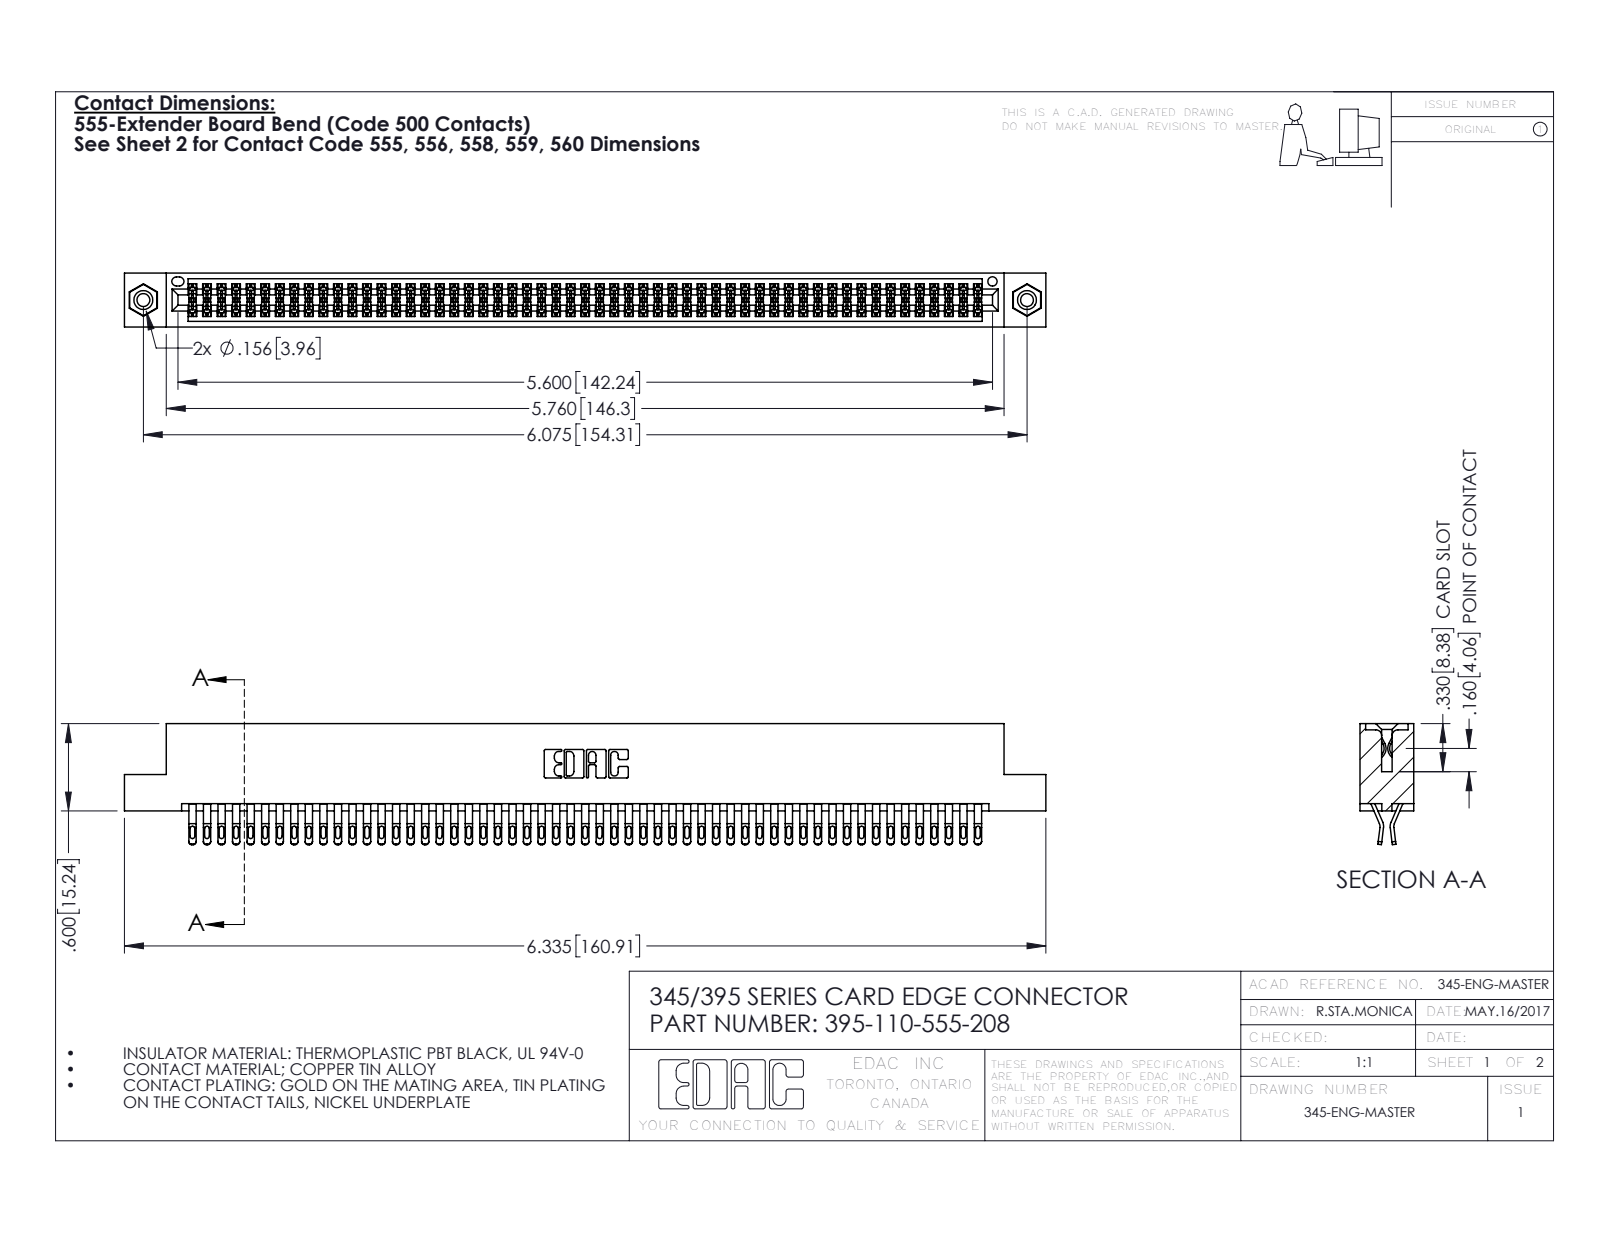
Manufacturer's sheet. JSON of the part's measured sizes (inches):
{"part_name": "345-250-001_345-250-003-102; 395-110-555-208; 345 Part_Flush Mounting Lugs - 0.156 Dia-TI; 345-292-001_555 Tail", "step_written_by": "SolidWorks 2016 (CONFIG_CONTROL_DESIGN)", "units": "inches", "bodies": {"solids": 113, "faces": 6346, "planar": 3522, "cylindrical": 2808, "other": 16}, "overall_size": [6.335, 0.832, 0.37], "volume_in3": 0.98, "surface_area_in2": 38.94, "round_holes": [[0.089, 2], [0.125, 2], [0.156, 2], [0.064, 1]], "round_bosses_or_shafts": [[0.155, 2]], "partial_cylinders_radius": [[0.016, 275], [0.02, 220], [0.006, 165], [0.01, 22], [0.007, 6], [0.031, 6], [0.026, 3], [0.01, 2]], "face_to_face_distances": [0.072, 0.298, 0.025, 0.37, 0.2, 0.098, 0.272, 0.225, 0.175, 0.149], "hole_center_spacings": [0.27, 5.839, 6.075]}
